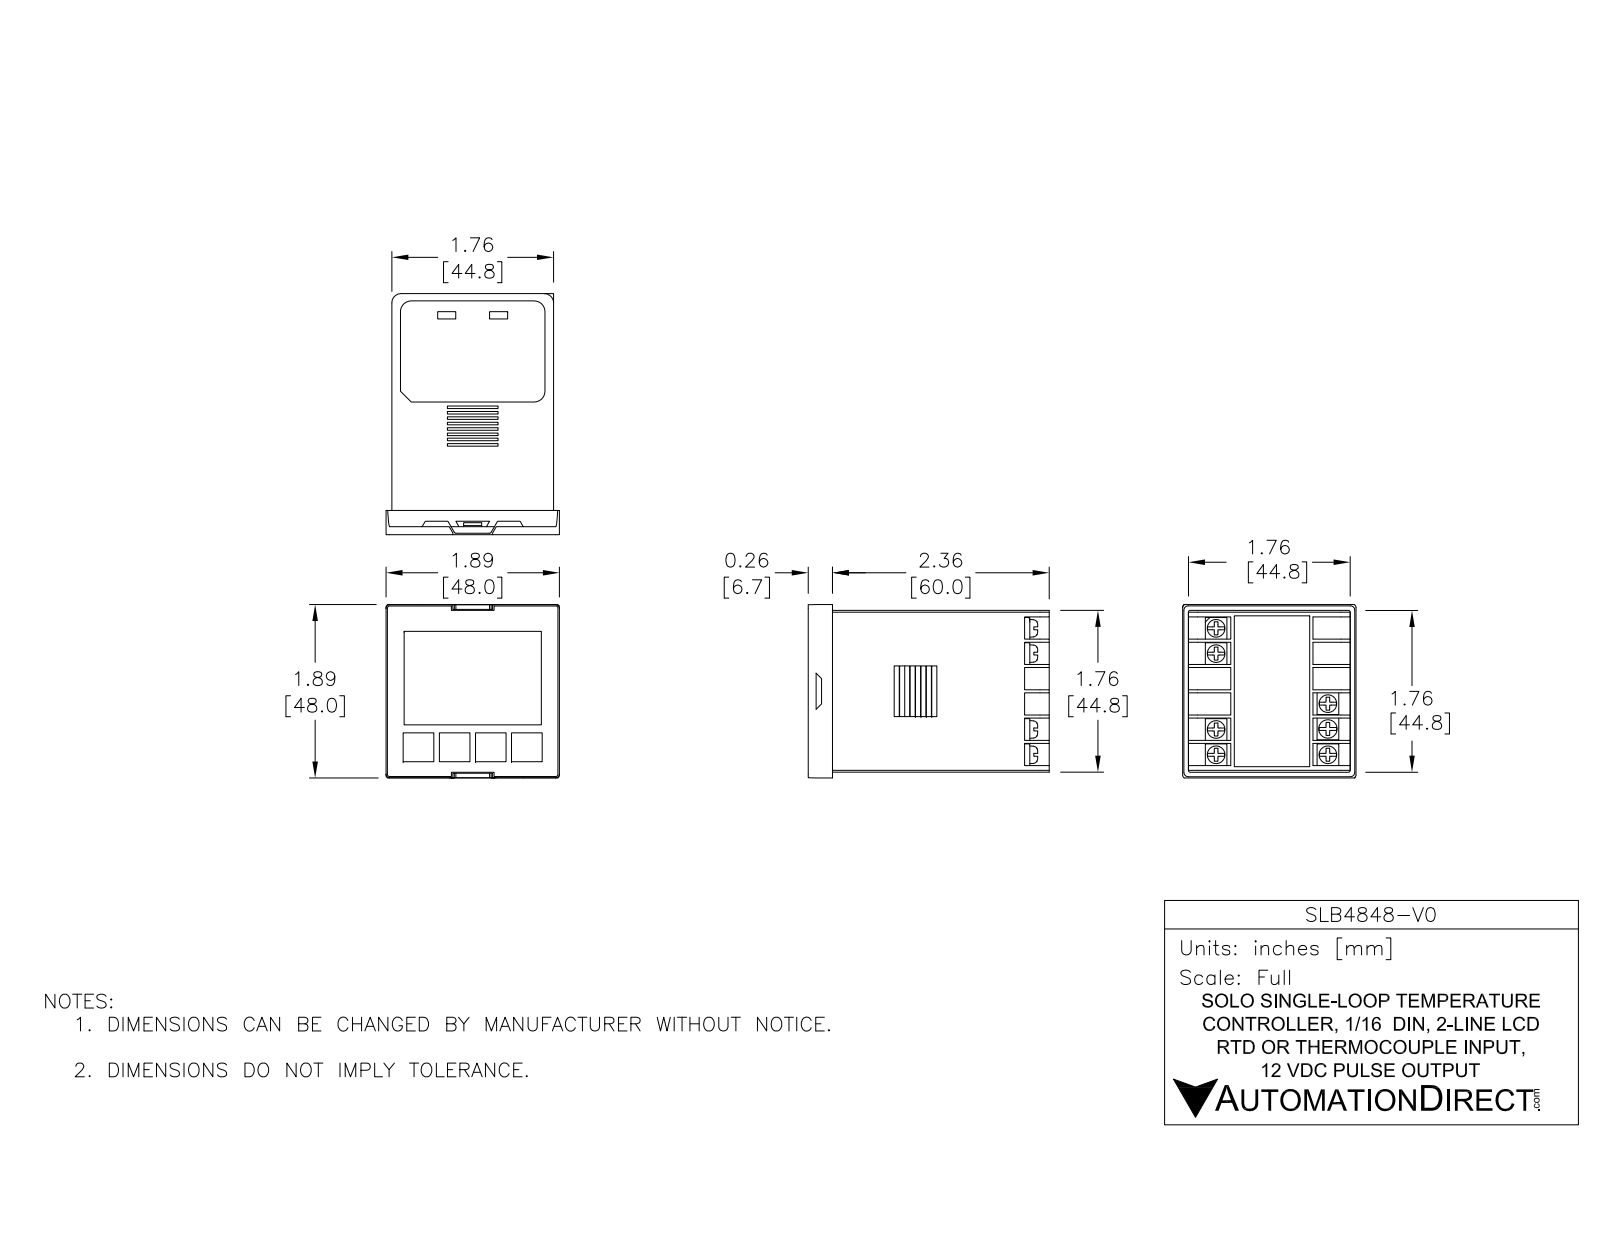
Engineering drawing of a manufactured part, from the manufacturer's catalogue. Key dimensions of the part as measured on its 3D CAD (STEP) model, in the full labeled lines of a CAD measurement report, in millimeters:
Part name (STEP PRODUCT): SLB4848-V0
STEP written by: SolidWorks 2017 (AUTOMOTIVE_DESIGN)
Units: millimetres
Bodies: 5 solids, 3364 faces (3117 planar, 141 cylindrical, 106 other)
Overall size (bounding box): 66.8 × 56.7 × 48
Volume: 125 900 mm³ · Surface area: 30 030 mm²
Round bosses / shafts (diameter × count): ⌀5.3 ×2, ⌀2.9 ×2
Partial cylindrical surfaces — rounded edges, fillets, slot ends (radius × count): R0.2 ×36, R0.2 ×8, R0.5 ×6, R1 ×6, R0.6 ×4, R1 ×4, R1.6 ×4, R4 ×4
Main face-to-face distances: 44.8, 1.2, 46.1, 0.4, 44.3, 1.3, 44.8, 44.8, 44.8, 46
